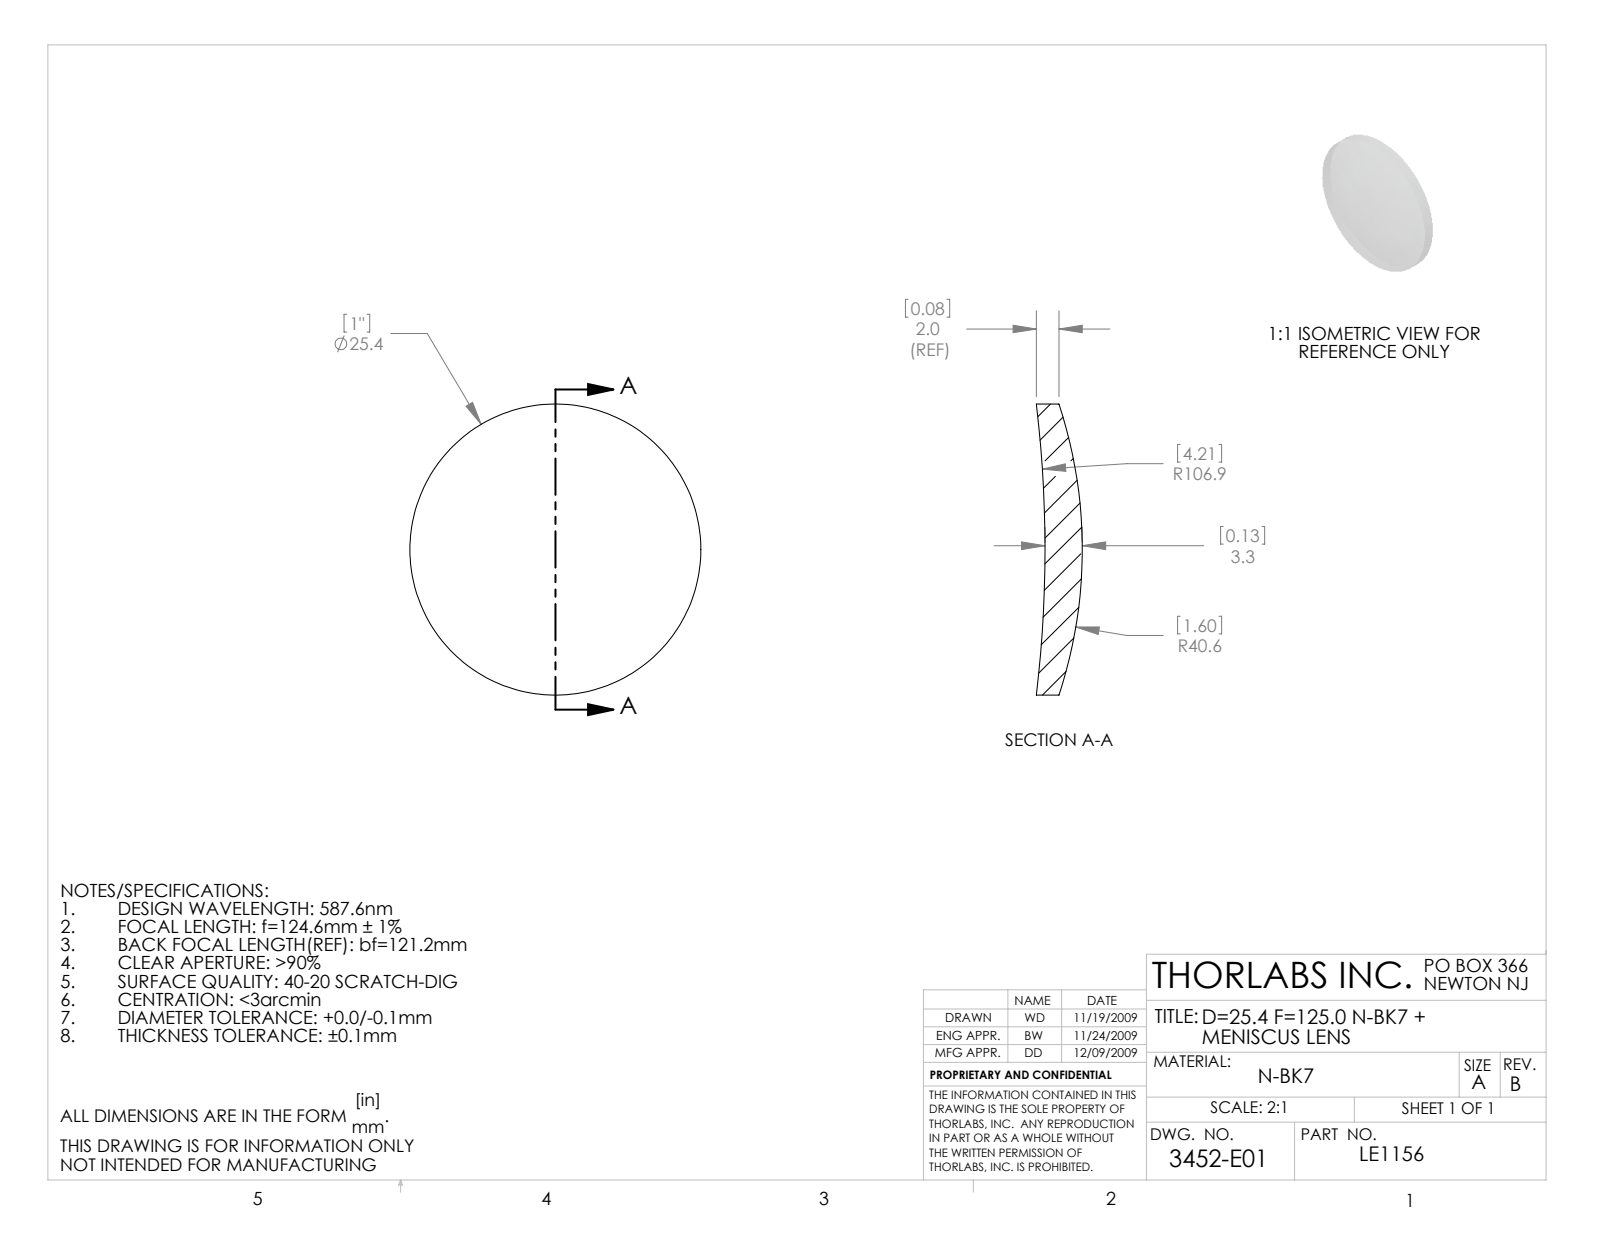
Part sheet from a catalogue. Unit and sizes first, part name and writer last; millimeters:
Units: millimetres
Overall size (bounding box): 25.4 × 25.4 × 4.02
Round bosses / shafts (diameter × count): ⌀25.4 ×1
Volume: 1 332 mm³ · Surface area: 1 186 mm²
Bodies: 1 solid, 6 faces (0 planar, 2 cylindrical, 4 other)
Part name (STEP PRODUCT): 3452-E0W
STEP written by: SolidWorks 2009 (AUTOMOTIVE_DESIGN)
